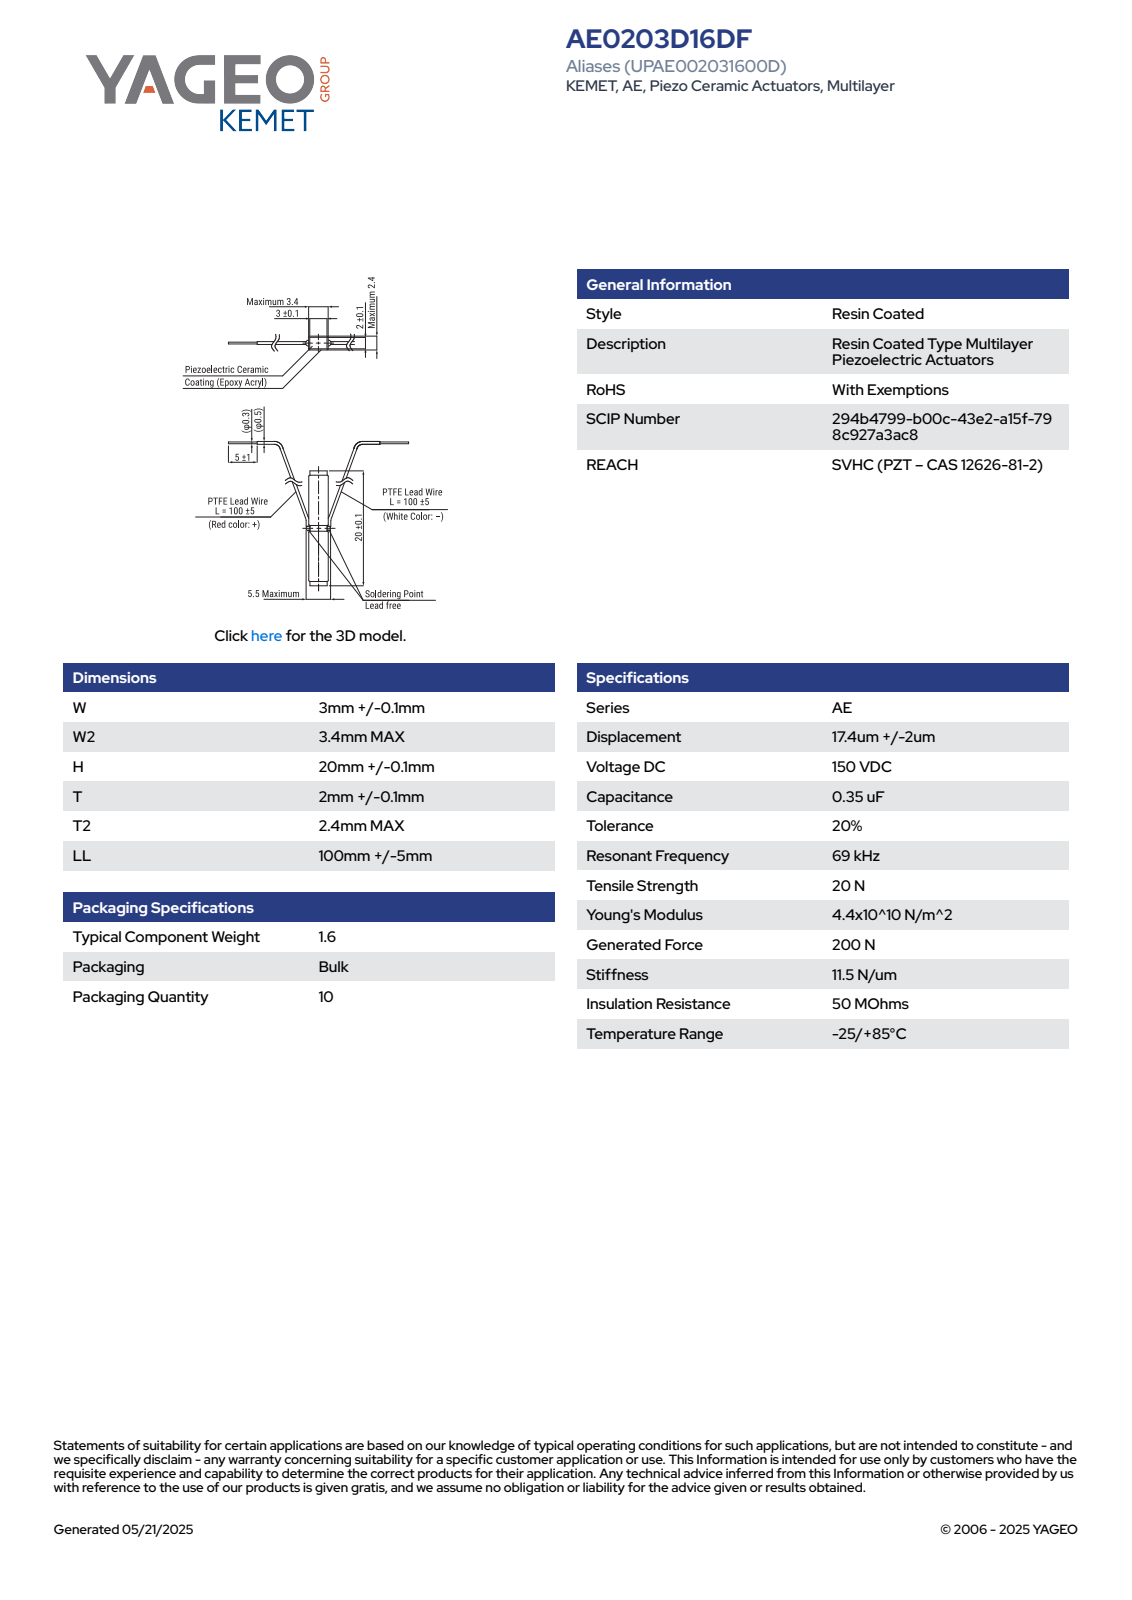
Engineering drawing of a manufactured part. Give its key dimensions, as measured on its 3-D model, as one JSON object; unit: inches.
{"part_name": "AL_KAE1_W3.1W23.4H20.1T2.1T22.4", "step_written_by": "SolidWorks 2014 (AUTOMOTIVE_DESIGN)", "units": "inches", "bodies": {"solids": 4, "faces": 93, "planar": 85, "cylindrical": 8, "other": 0}, "overall_size": [0.792, 0.134, 0.094], "volume_in3": 0.008, "surface_area_in2": 0.357, "partial_cylinders_radius": [[0.006, 8]], "face_to_face_distances": [0.089, 0.118, 0.083, 0.114, 0.094, 0.122, 0.791, 0.318, 0.473, 0.078]}
